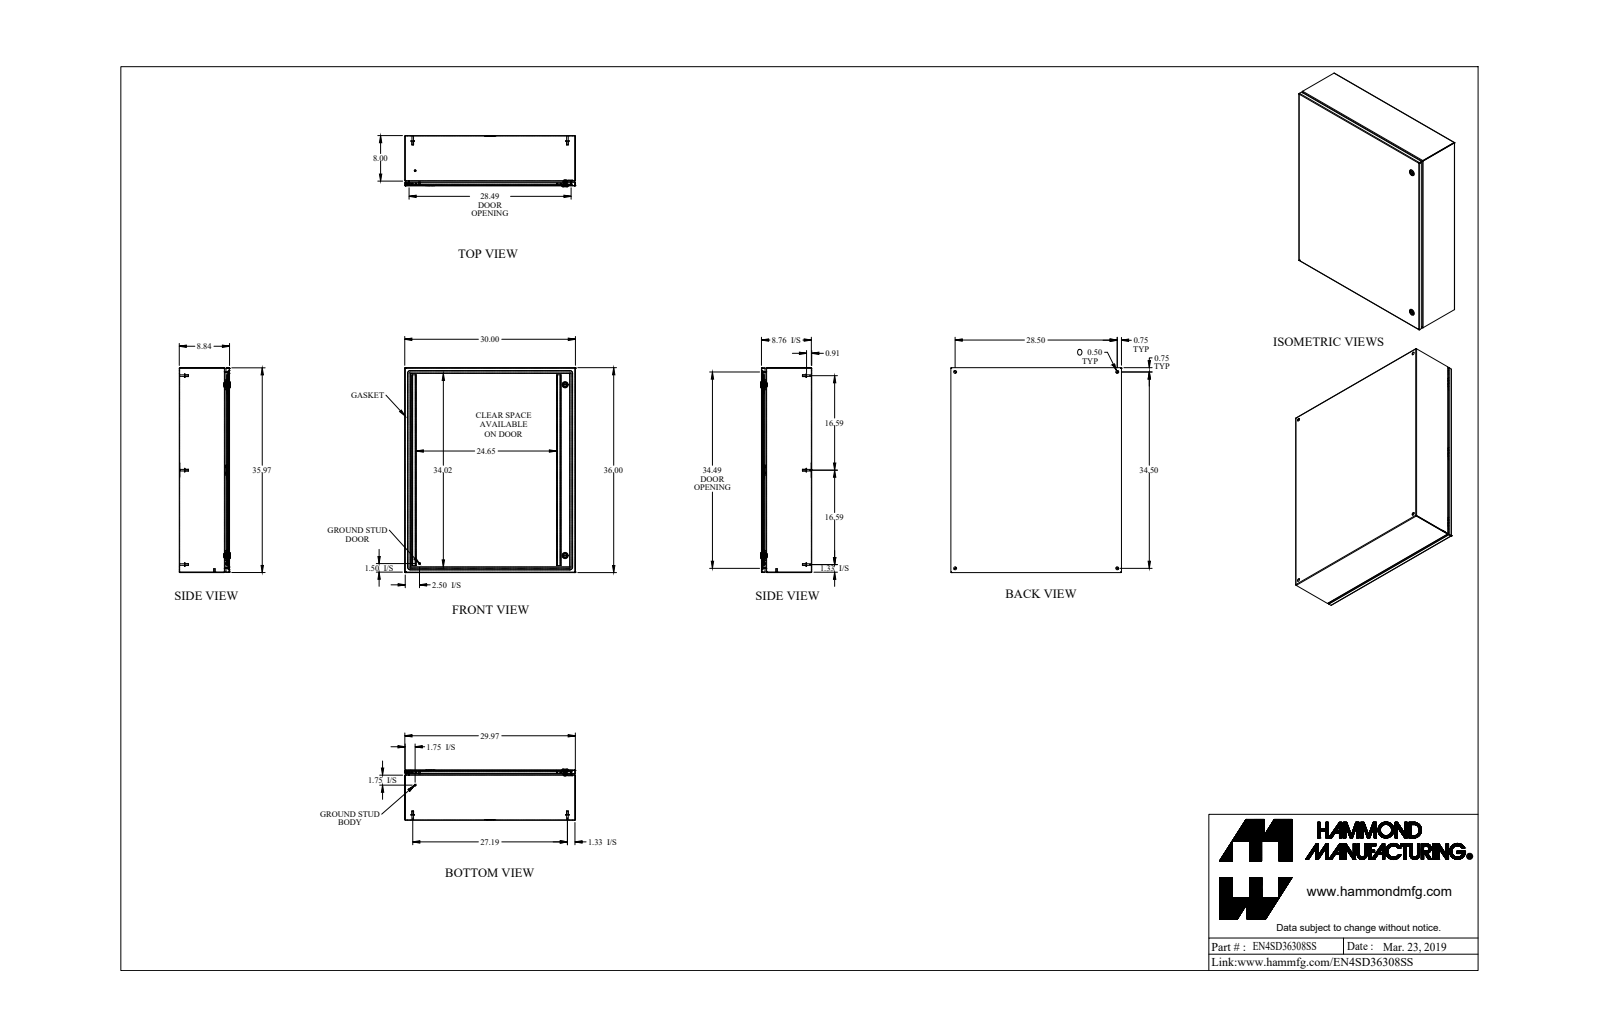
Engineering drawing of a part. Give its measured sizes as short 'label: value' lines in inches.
name: EN4SD36308SS_Default
written by: SolidWorks 2019 (CONFIG_CONTROL_DESIGN)
unit: in
bodies: 35 solids, 959 faces (458 planar, 313 cylindrical, 188 other)
size: 36 × 30 × 9.002
volume: 267.6 in³; area: 7 508 in²
holes: 6× ⌀0.5, 2× ⌀0.197, 2× ⌀0.387, 2× ⌀0.63, 2× ⌀0.768, 1× ⌀0.172, 1× ⌀0.24, 1× ⌀0.242
bosses: 8× ⌀0.625, 8× ⌀0.313, 6× ⌀0.275, 2× ⌀1.1, 2× ⌀0.785, 2× ⌀0.525, 2× ⌀0.25, 2× ⌀0.236
rounds: 20× R0.036, 20× R0.108, 16× R0.25, 12× R0.01, 12× R0.048, 6× R0.006, 6× R0.062, 4× R0.125
face distances: 0.072, 8.77, 8.698, 8.842, 29.928, 35.928, 29.856, 30, 35.856, 36
hole spacings: 27.531, 28.5, 34.5, 44.749, 2.487, 2.488, 30, 32.267
